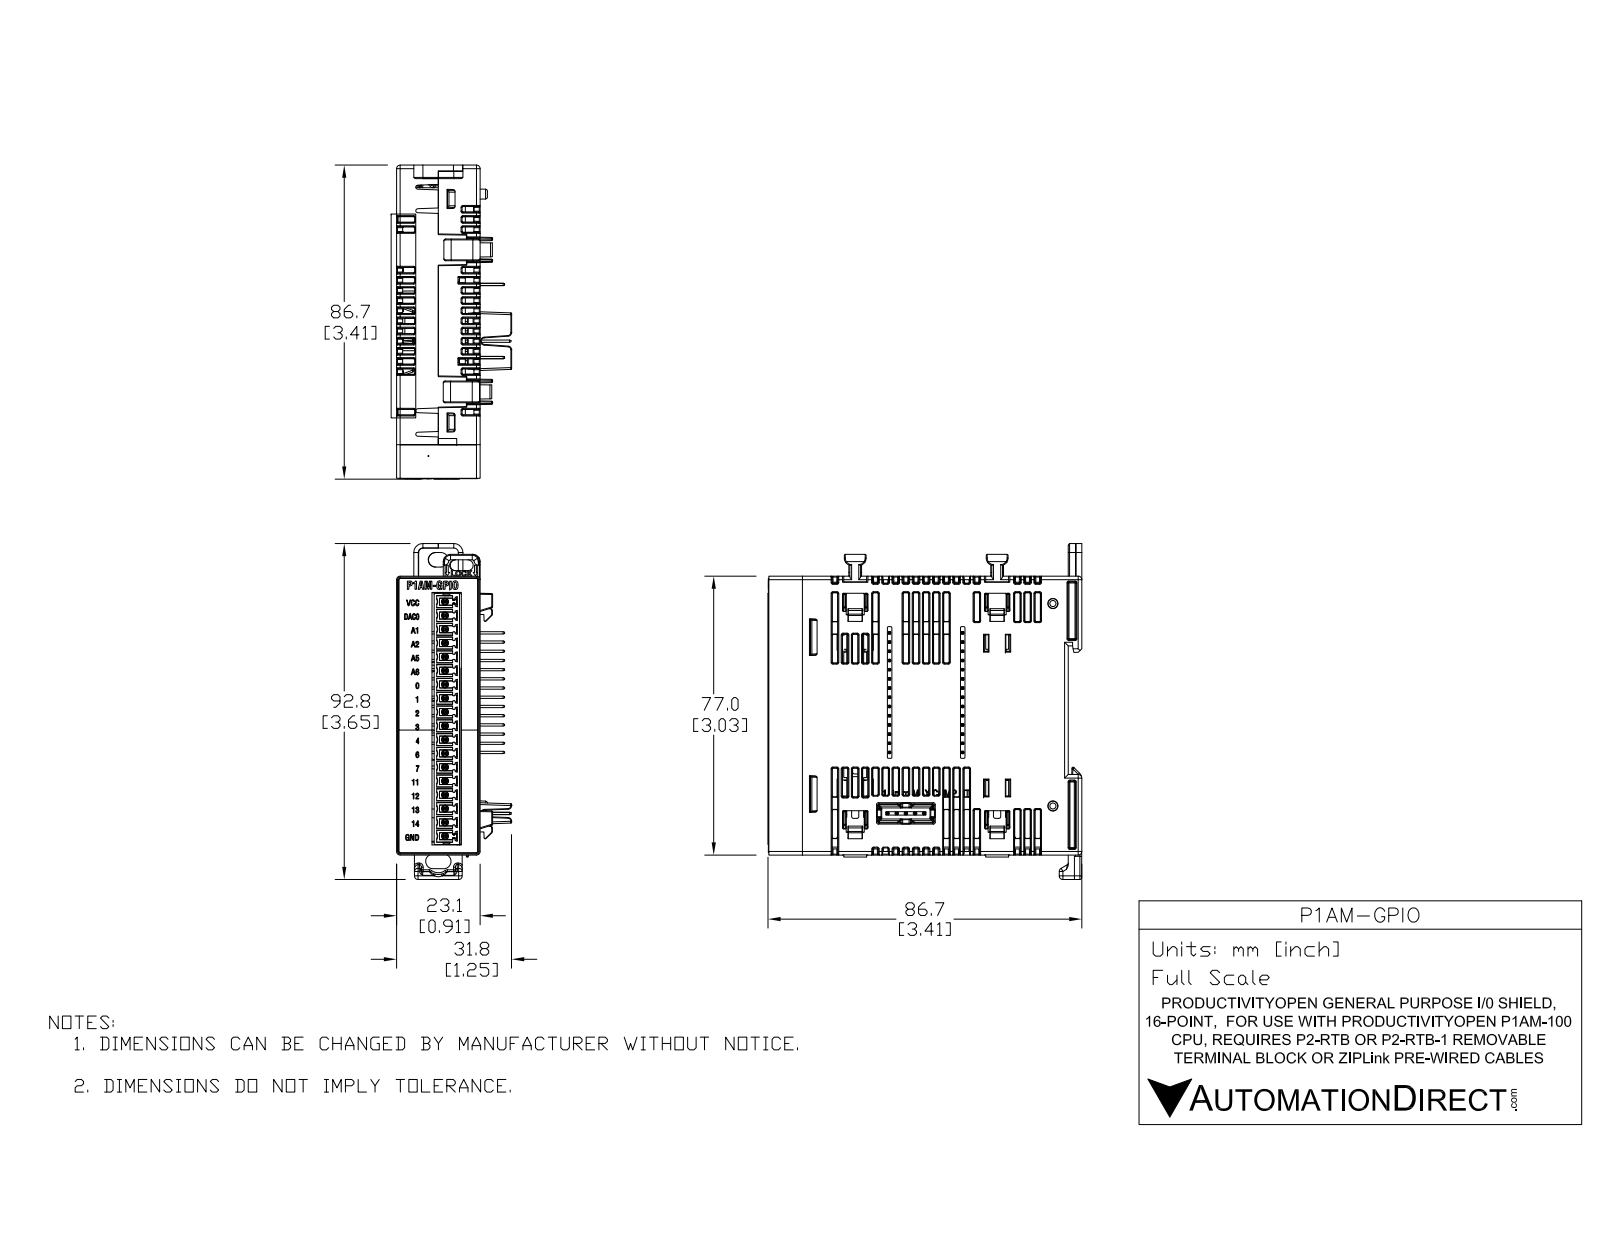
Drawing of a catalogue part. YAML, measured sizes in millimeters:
part_name: "P1AM-GPIO EXT w sketches MOD r1 TOP DIM a BODY FACE Comb Mate b 1C3 from XT 1B2r1 C1r1"
step_written_by: "SolidWorks 2017 (AUTOMOTIVE_DESIGN)"
units: millimeters
bodies: {solids: 38, faces: 4872, planar: 3537, cylindrical: 663, other: 672}
overall_size: [92.8, 86.7, 31.8]
volume: 143200
surface_area: 42210
round_holes:
  - {diameter: 0.3, count: 33}
  - {diameter: 0.4, count: 16}
  - {diameter: 0.4, count: 2}
  - {diameter: 3.1, count: 2}
partial_cylinders:
  - {radius: 0.5, count: 158}
  - {radius: 0.3, count: 95}
  - {radius: 0.2, count: 74}
  - {radius: 1, count: 30}
  - {radius: 1, count: 23}
  - {radius: 1.6, count: 18}
  - {radius: 2, count: 11}
  - {radius: 0.3, count: 8}
face_to_face_distances: [23, 77, 8.9, 1.7, 21.4, 9.4, 22.8, 3.8, 0.5, 73.4]
hole_center_spacings: [2.5, 5.1, 7.6, 20.4, 10.2, 20.8, 21.6, 12.7]
